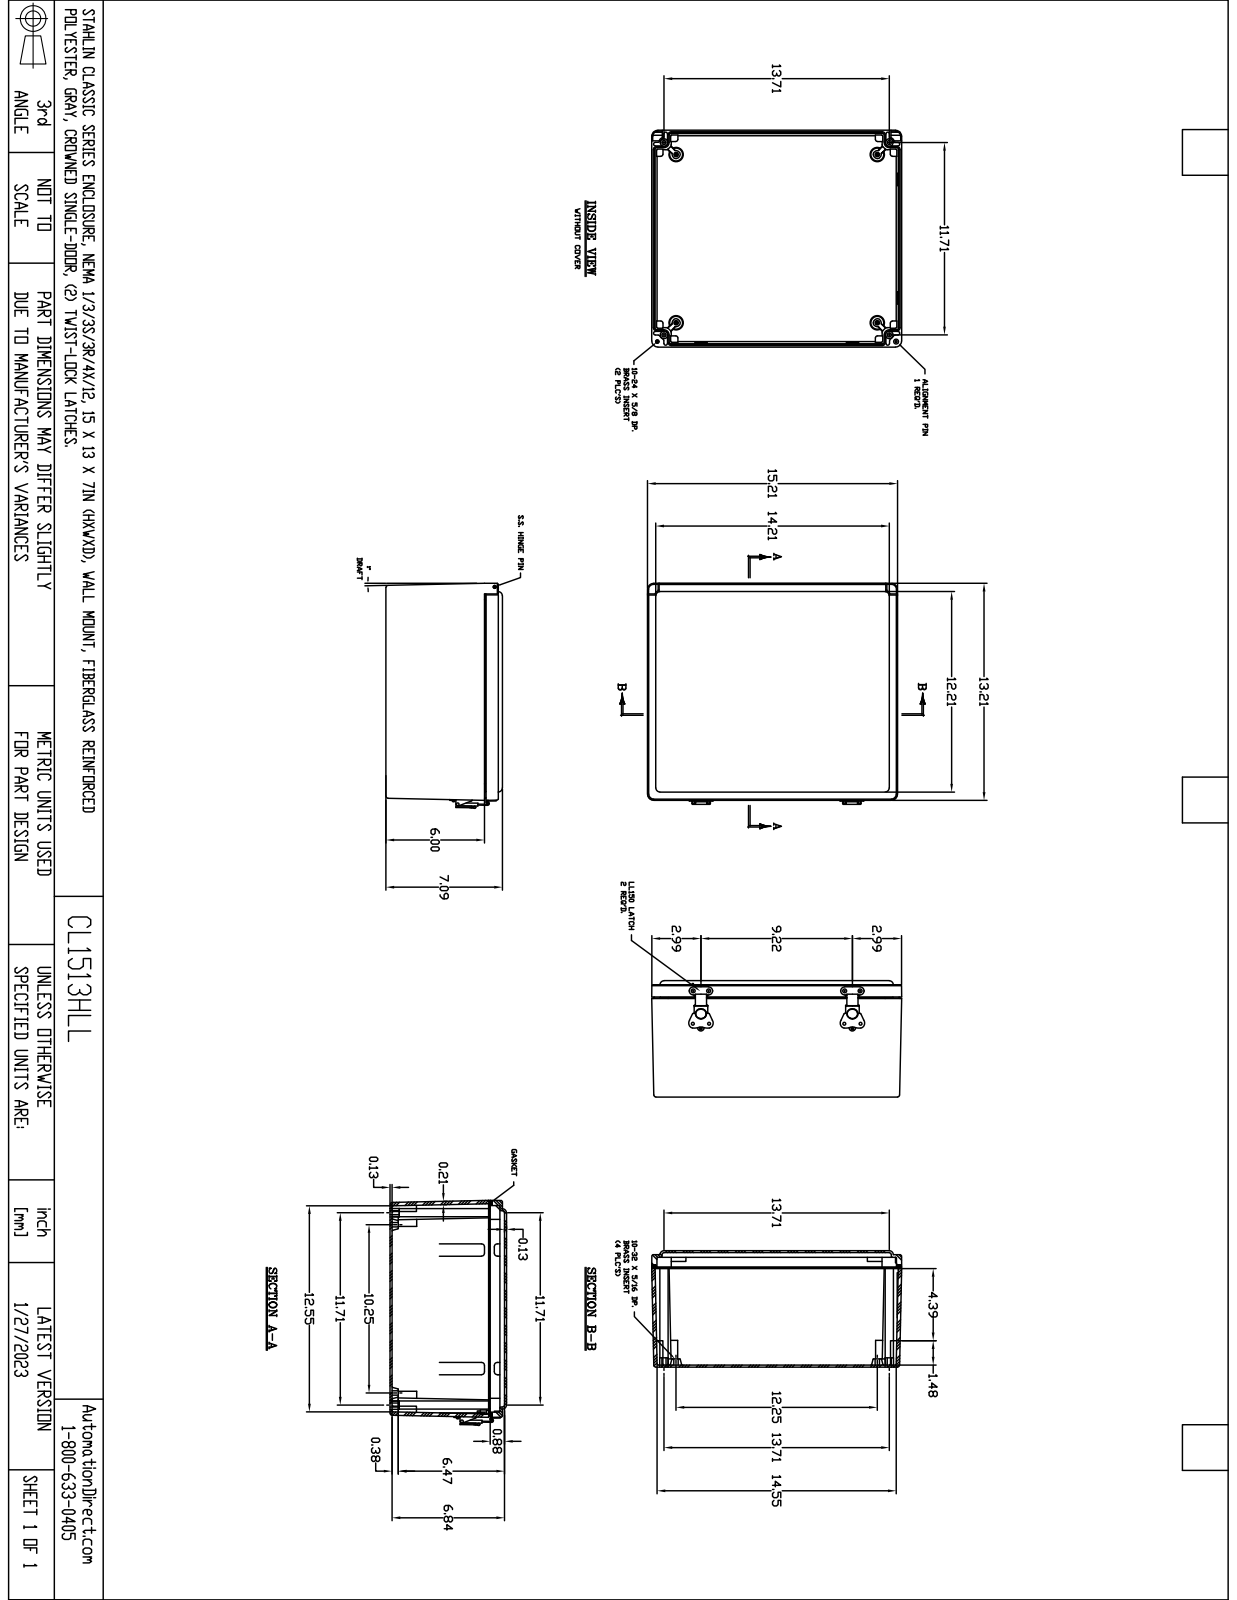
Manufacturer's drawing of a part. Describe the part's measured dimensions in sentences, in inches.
The part is named "CE1513HLL". Its 3-D file was written by "SolidWorks 2018 (AUTOMOTIVE_DESIGN)". It is 41 solids with 1486 faces: 525 planar, 542 cylindrical and 419 other. Overall it measures 15.22 by 13.724 by 7.094 inches. Its volume is 139.8 cubic inches and its surface area 1 706 square inches. Round holes: 8 of diameter 0.104, 8 of diameter 0.14, 6 of diameter 0.281, 5 of diameter 0.187, 4 of diameter 0.13, 4 of diameter 0.156, 4 of diameter 0.313, 4 of diameter 0.531, 2 of diameter 0.096, 2 of diameter 0.145, 2 of diameter 0.156, 2 of diameter 0.219. Round bosses or shafts: 2 of diameter 0.6, 2 of diameter 0.375, 2 of diameter 0.234, 2 of diameter 0.178, 2 of diameter 0.095, 2 of diameter 0.088, 1 of diameter 0.371, 1 of diameter 0.299. Partial cylindrical surfaces (rounded edges, fillets, slot ends): 71 of radius 0.02, 71 of radius 0.031, 41 of radius 0.125, 28 of radius 0.01, 23 of radius 0.062, 12 of radius 0.25, 11 of radius 0.313, 10 of radius 0.188. The main face-to-face distances are 0.125, 6.969, 0.186, 7.094, 6.844, 0.125, 0.25, 6.844, 6.719, 0.75. The hole center spacings are 9.187, 0.506, 0.841, 1.039, 11.01, 13.007, 17.009, 0.528.
